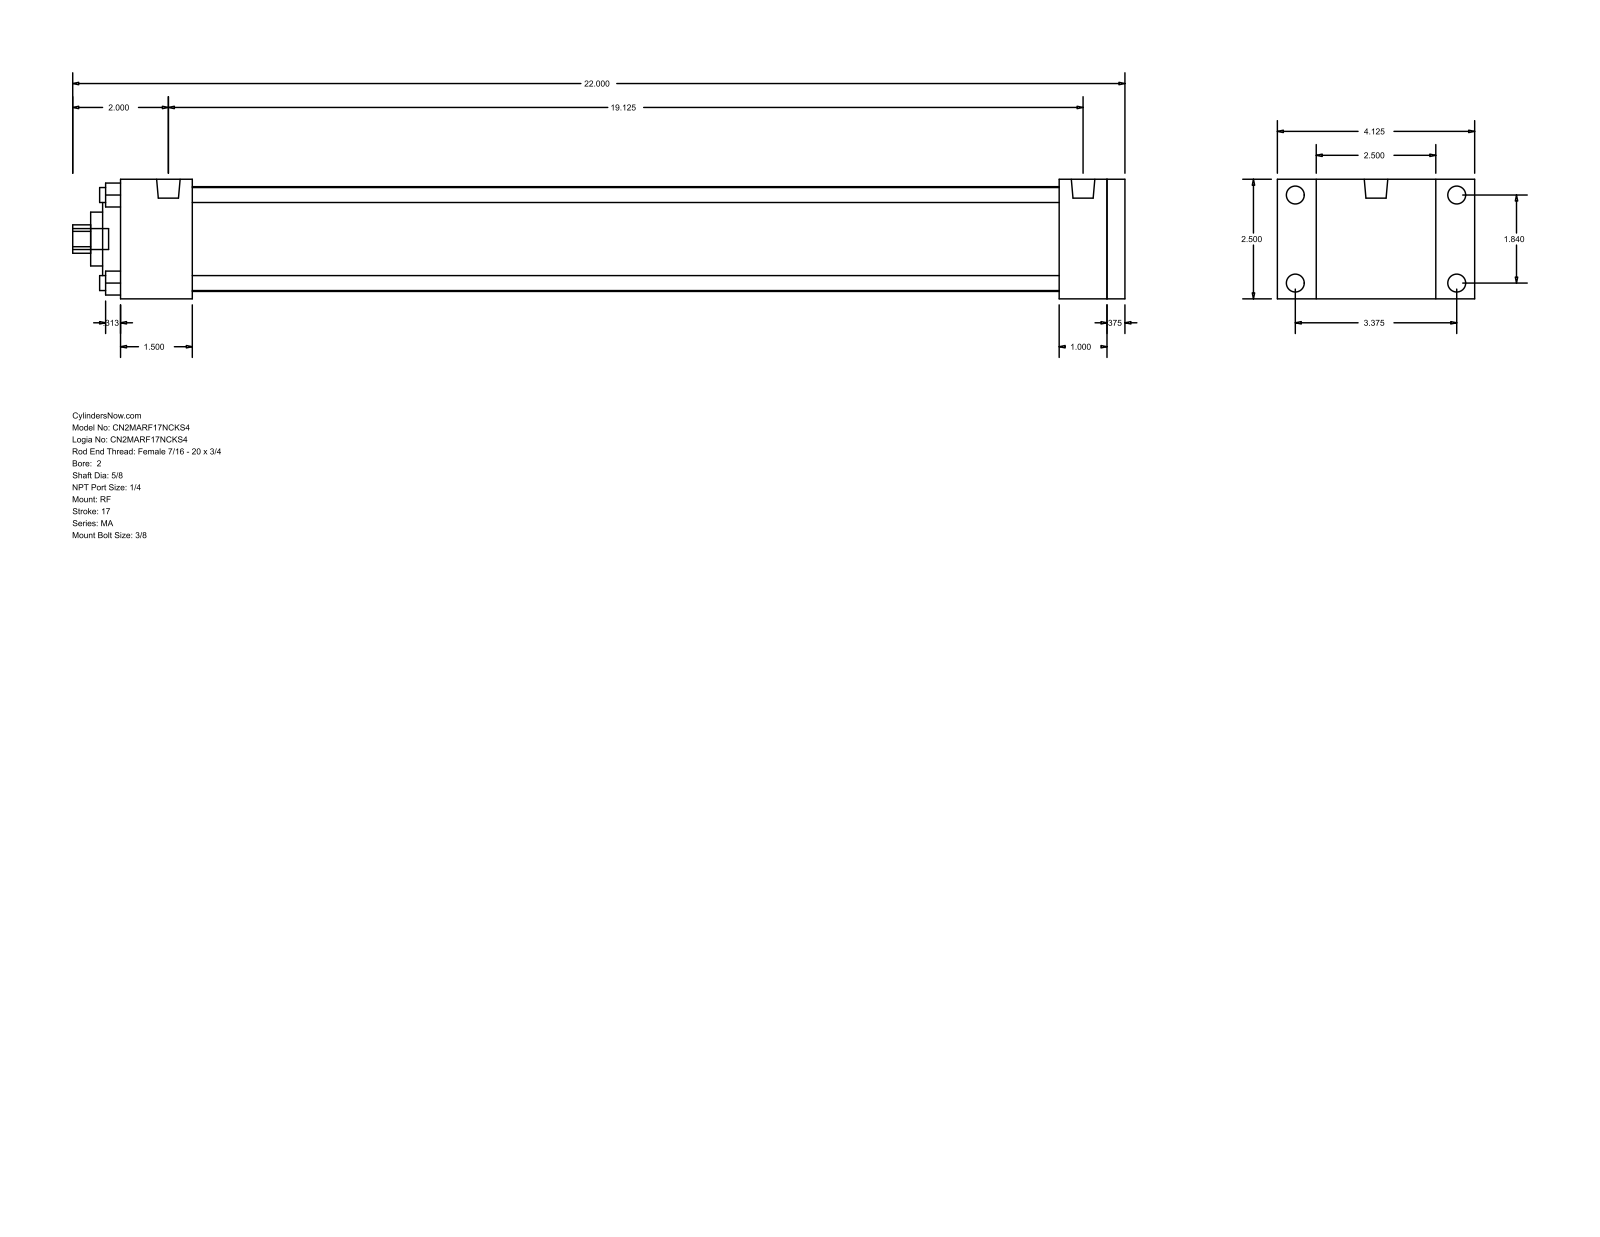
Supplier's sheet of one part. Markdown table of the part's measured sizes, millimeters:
| quantity | value |
| --- | --- |
| part name | MA_RF__0200_0.625 |
| STEP written by | GSSL Pune (CONFIG_CONTROL_DESIGN) |
| units | millimeters |
| bodies | 0 solids, 94 faces (65 planar, 29 cylindrical, 0 other) |
| overall size | 558.8 × 104.78 × 63.5 |
| round holes (diameter × count) | 7.94 × 4, 15.88 × 1, 28.57 × 1, 50.8 × 1, 55.63 × 1 |
| round bosses / shafts (diameter × count) | 9.53 × 4, 7.94 × 4, 12.49 × 2, 11.11 × 1 |
| partial cylindrical surfaces (radius × count) | 7.54 × 1 |
| main face-to-face distances | 63.5, 9.53, 38.1, 9.52, 523.87, 533.4, 542.92, 485.77, 495.3, 498.48 |
| hole center spacings | 33.05, 46.74, 66.1 |
